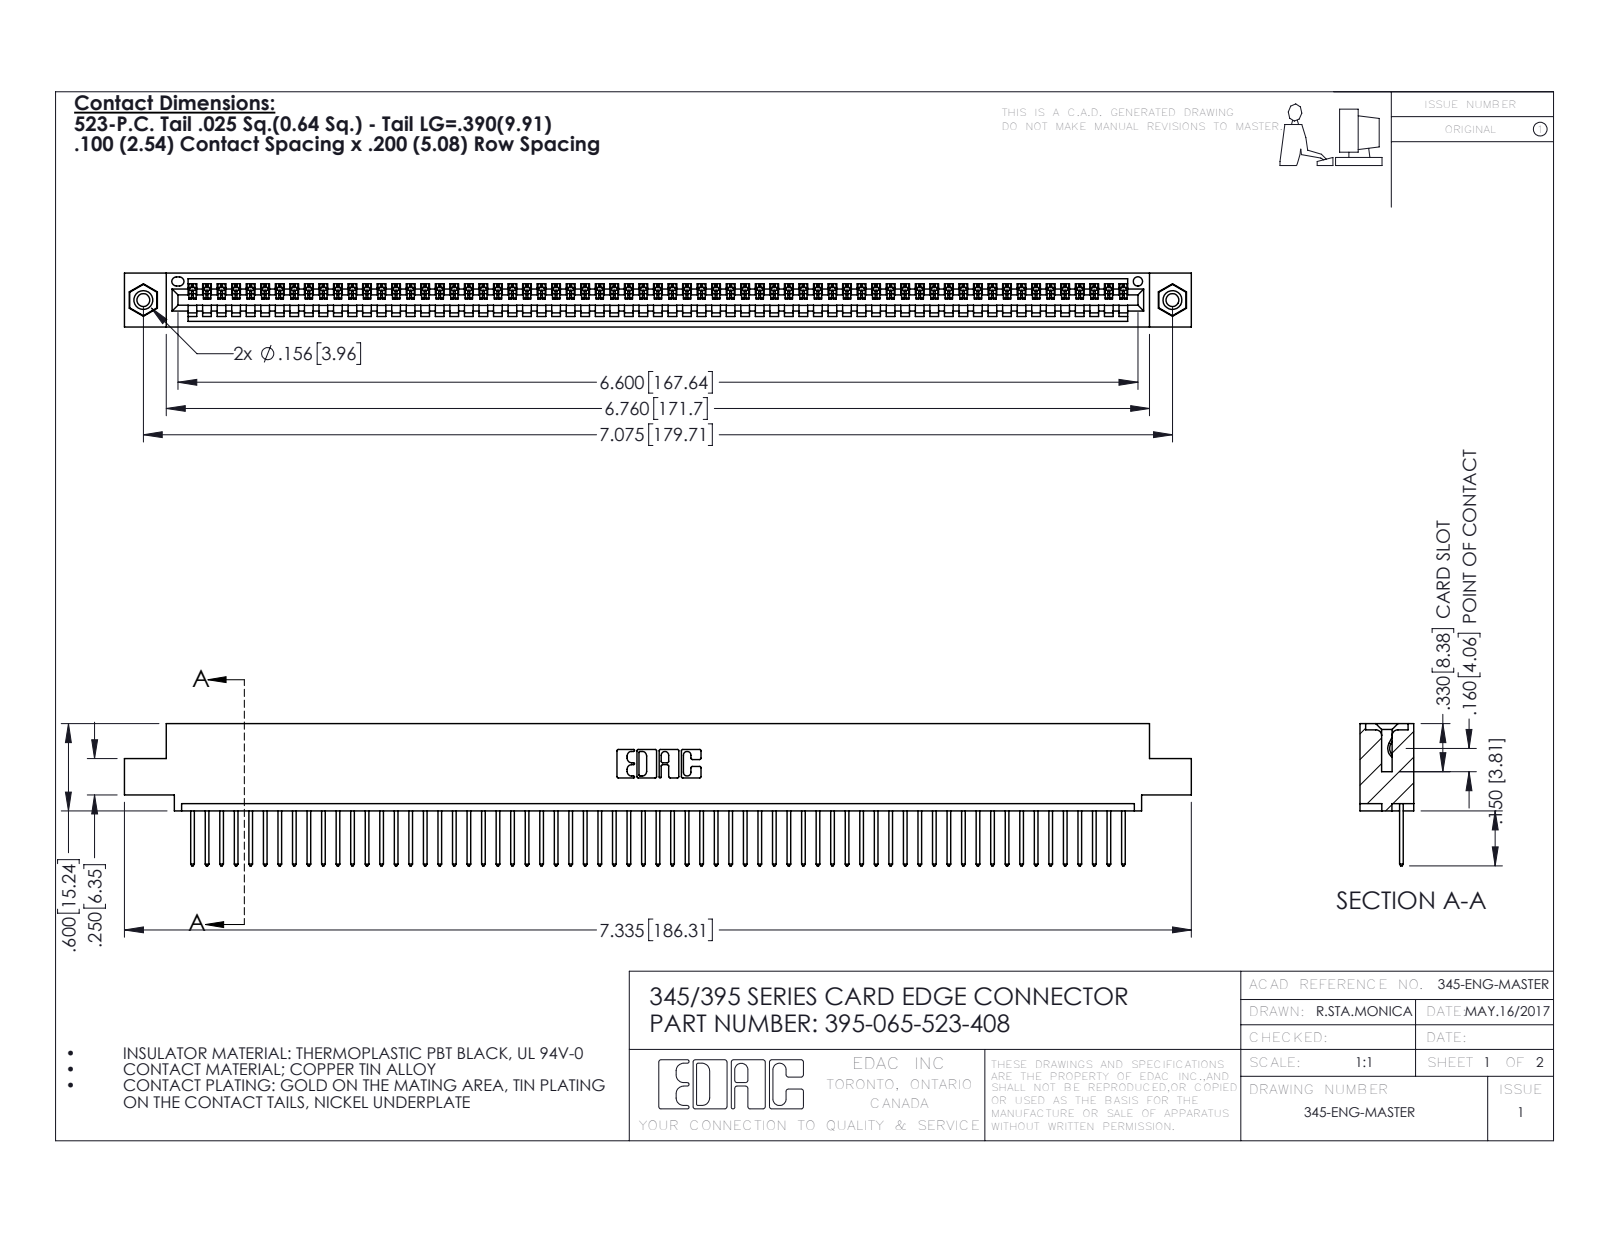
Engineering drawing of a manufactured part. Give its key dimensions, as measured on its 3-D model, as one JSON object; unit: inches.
{"part_name": "345 Part_0.110 Offset - 0.156 Dia-TI; 395-065-523-408; 345-250-001_345-250-003-102; 345-292-001_345-293-123", "step_written_by": "SolidWorks 2016 (CONFIG_CONTROL_DESIGN)", "units": "inches", "bodies": {"solids": 68, "faces": 3960, "planar": 2716, "cylindrical": 1228, "other": 16}, "overall_size": [7.335, 0.977, 0.37], "volume_in3": 1.085, "surface_area_in2": 37.37, "round_holes": [[0.089, 2], [0.125, 2], [0.156, 2], [0.064, 1]], "round_bosses_or_shafts": [[0.155, 2]], "partial_cylinders_radius": [[0.006, 130], [0.01, 130], [0.01, 22], [0.007, 6], [0.031, 6], [0.026, 3], [0.031, 2], [0.04, 2]], "face_to_face_distances": [0.072, 0.298, 0.37, 0.2, 0.098, 0.272, 0.025, 0.225, 0.149, 0.072], "hole_center_spacings": [0.27, 6.839, 7.075]}
